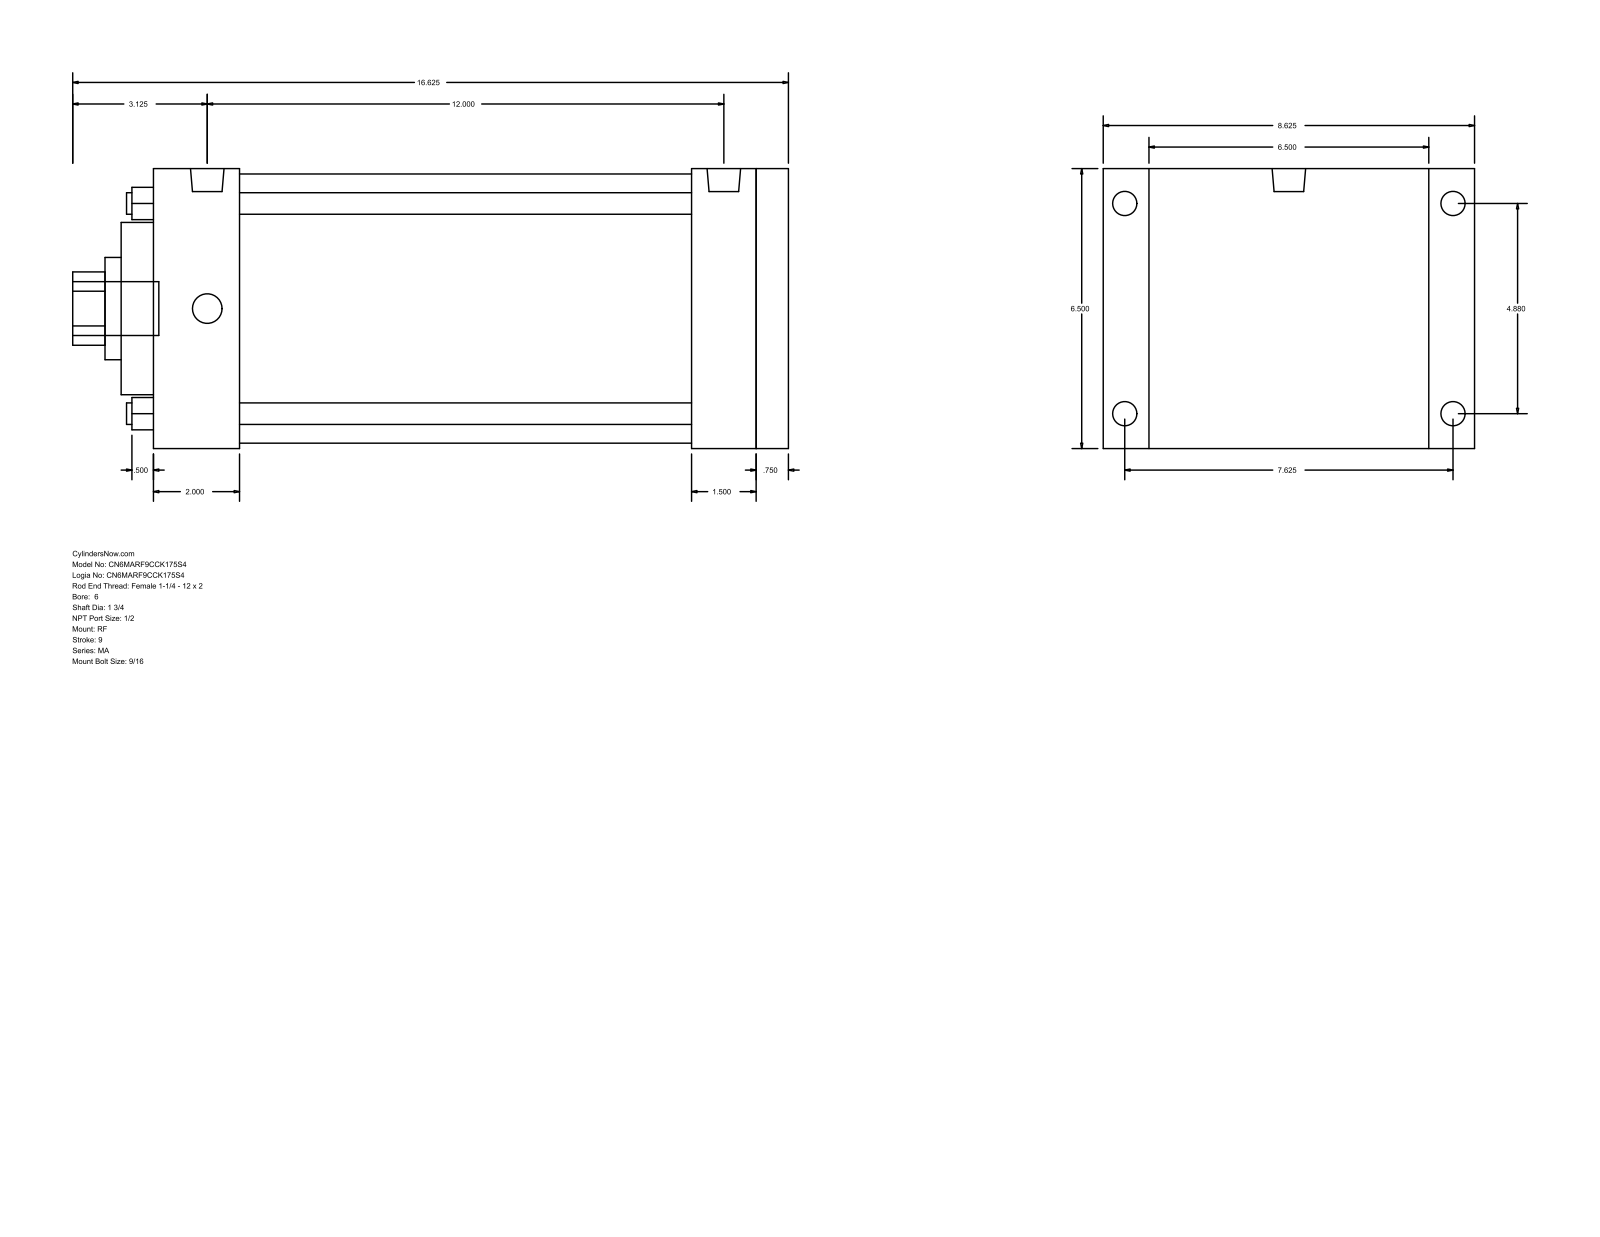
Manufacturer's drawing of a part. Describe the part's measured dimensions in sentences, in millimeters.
The part is named "MA_RF__0600_1.75". Its 3-D file was written by "GSSL Pune (CONFIG_CONTROL_DESIGN)". It is 0 solids with 94 faces: 65 planar, 29 cylindrical and 0 other. Overall it measures 422.27 by 219.07 by 165.1 millimeters. Round holes: 4 of diameter 12.7, 1 of diameter 44.45, 1 of diameter 60.33, 1 of diameter 101.6, 1 of diameter 158.75. Round bosses or shafts: 4 of diameter 17.46, 4 of diameter 14.29, 2 of diameter 19.77, 1 of diameter 31.75. Partial cylindrical surfaces (rounded edges, fillets, slot ends): 1 of radius 21.63. The main face-to-face distances are 165.1, 374.65, 19.04, 355.61, 19.05, 50.8, 304.81, 323.85, 317.5, 266.7. The hole center spacings are 87.65, 123.96, 175.31.
